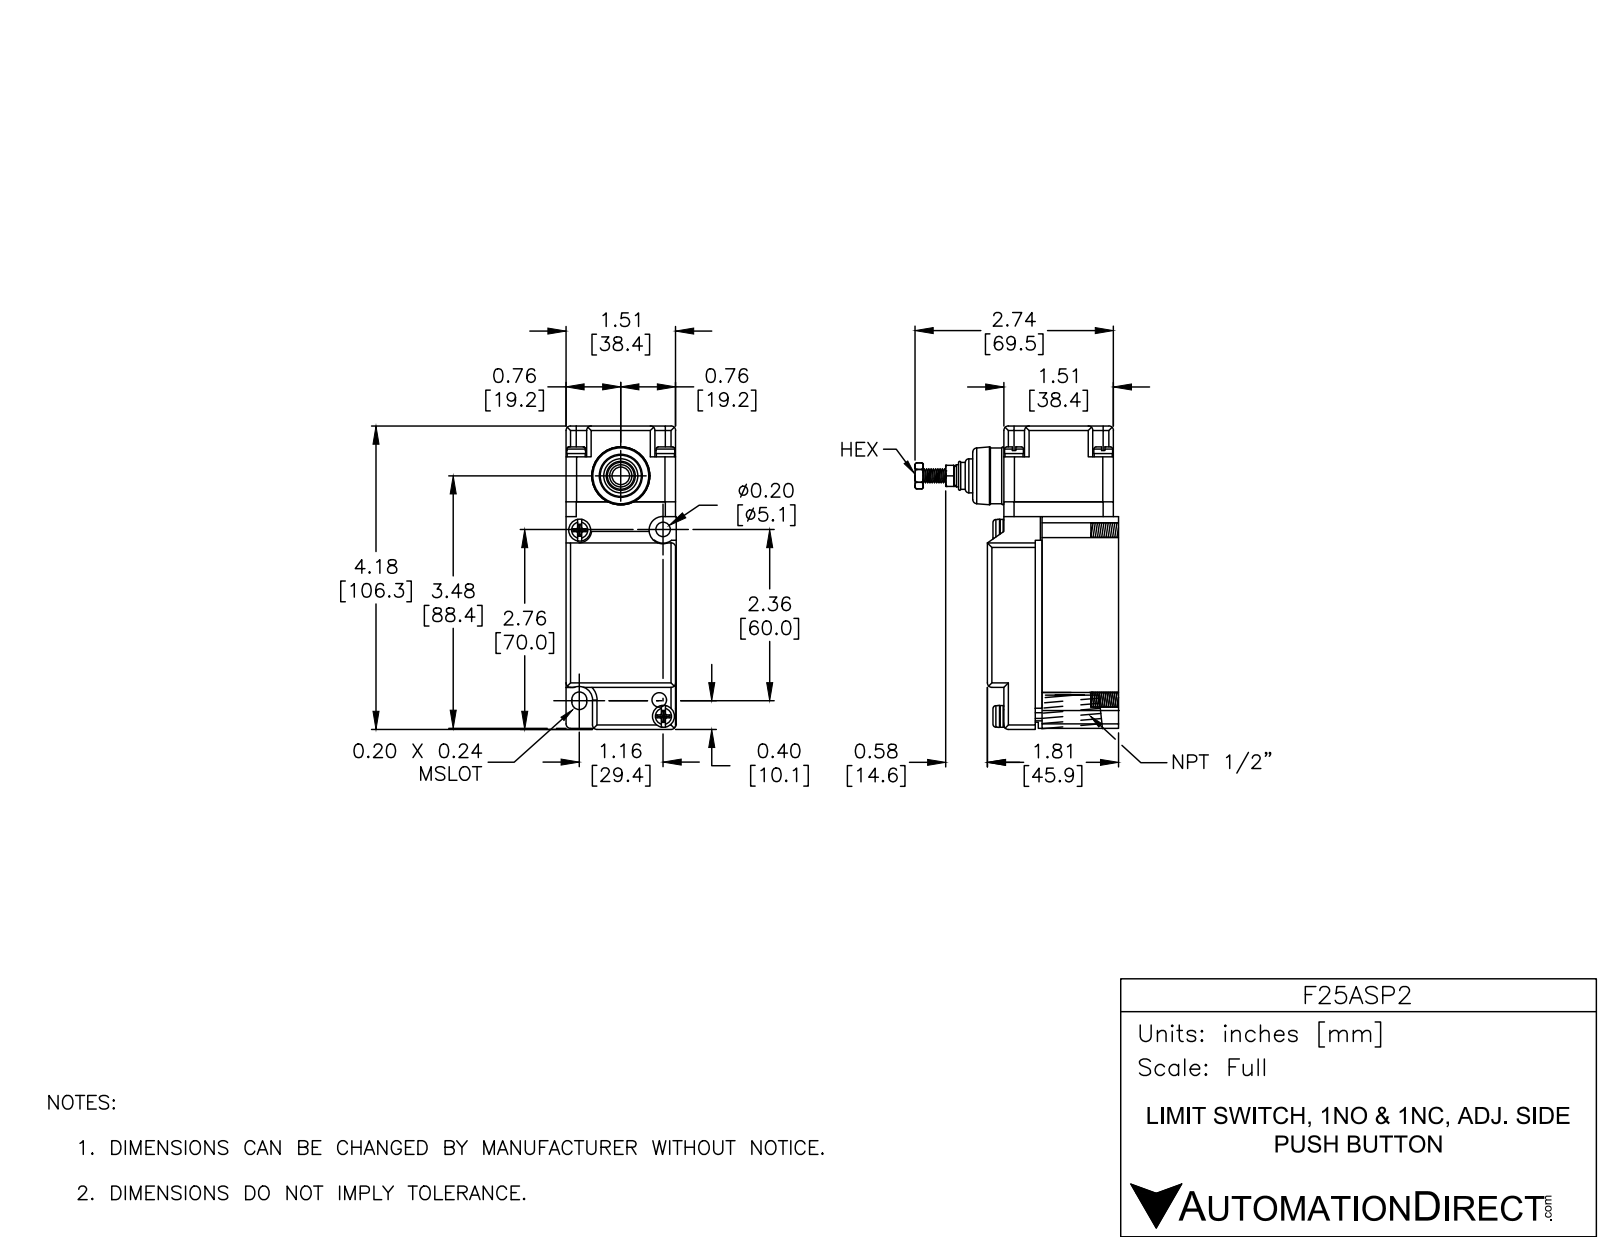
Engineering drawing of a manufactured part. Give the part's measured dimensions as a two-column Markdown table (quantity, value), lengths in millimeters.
| quantity | value |
| --- | --- |
| part name | F25ASP2; Imported12; Imported15; Imported14 (+8 more) |
| STEP written by | SolidWorks 2002296 (CONFIG_CONTROL_DESIGN) |
| units | millimeters |
| bodies | 14 solids, 831 faces (259 planar, 182 cylindrical, 390 other) |
| overall size | 106.3 × 71.3 × 38.6 |
| volume | 167 300 mm³ |
| surface area | 46 650 mm² |
| round holes (diameter × count) | 4.5 × 4, 4.8 × 3, 5.1 × 3, 2 × 1, 5.2 × 1, 5.8 × 1, 5.9 × 1, 6.6 × 1, 10.6 × 1, 14.7 × 1, 16 × 1, 18.3 × 1 |
| round bosses / shafts (diameter × count) | 6.6 × 4, 6.4 × 4, 3.6 × 4, 7.7 × 2, 7.6 × 2, 19.6 × 1, 16.6 × 1, 14.4 × 1 |
| partial cylindrical surfaces (radius × count) | 1.6 × 29, 0.8 × 16, 0.4 × 8, 3.7 × 8, 3.6 × 4, 2.6 × 2, 4.8 × 2, 4.8 × 2 |
| main face-to-face distances | 2.4, 29.2, 26.8, 38.6, 38.4, 16.8, 19.2, 45.9, 5.8, 11 |
| hole center spacings | 31.2, 31.2, 44.2, 71.5, 5.7, 6, 19.2, 19.2 |
